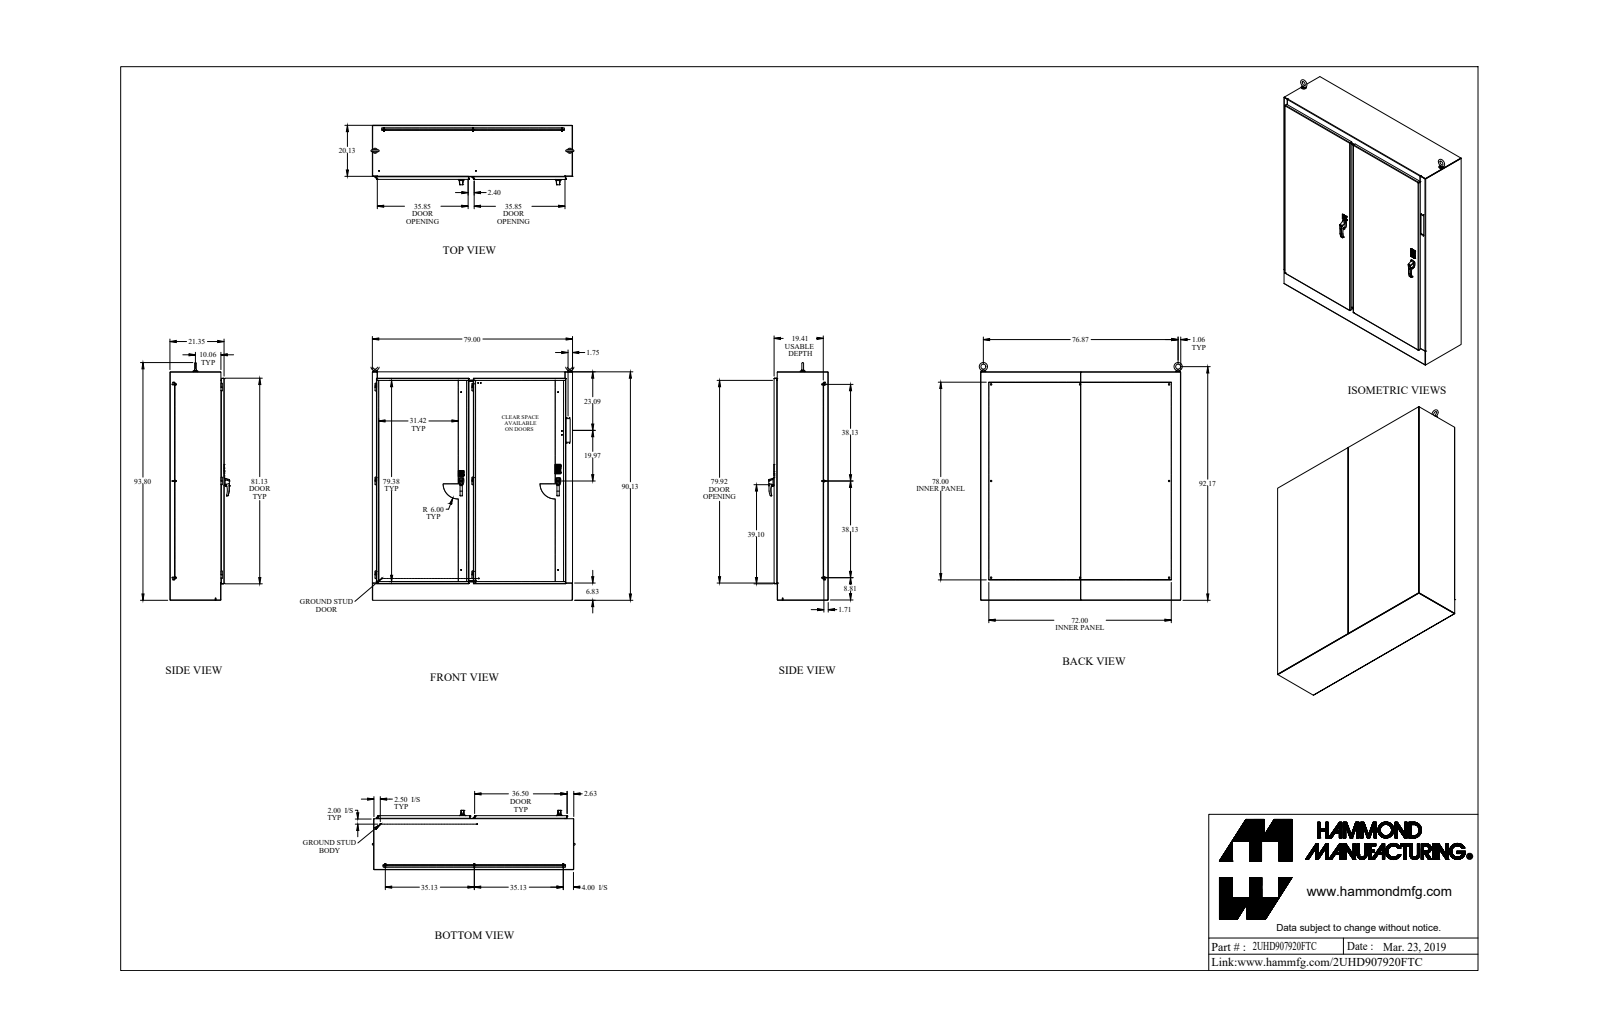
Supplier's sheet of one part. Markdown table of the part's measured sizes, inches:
| quantity | value |
| --- | --- |
| part name | 2UHD907920FTC |
| STEP written by | SolidWorks 2018 (AUTOMOTIVE_DESIGN) |
| units | inches |
| bodies | 215 solids, 3044 faces (1772 planar, 898 cylindrical, 374 other) |
| overall size | 93.799 × 80.122 × 23.466 |
| volume | 5 988 in³ |
| surface area | 62 430 in² |
| round holes (diameter × count) | 0.196 × 12, 0.281 × 11, 0.307 × 11, 0.25 × 10, 0.35 × 8, 0.257 × 6, 0.313 × 6, 0.445 × 5, 0.28 × 4, 0.282 × 4, 0.375 × 4, 0.39 × 4 |
| round bosses / shafts (diameter × count) | 0.25 × 19, 1 × 14, 0.65 × 9, 0.375 × 9, 0.33 × 9, 0.281 × 8, 0.75 × 6, 0.53 × 6 |
| partial cylindrical surfaces (radius × count) | 0.125 × 62, 0.06 × 53, 0.5 × 38, 0.185 × 32, 0.03 × 28, 0.017 × 16, 0.018 × 16, 0.032 × 12 |
| main face-to-face distances | 0.125, 0.072, 19.431, 21.369, 21.243, 1.937, 1.812, 1.865, 1.74, 19.503 |
| hole center spacings | 38.249, 1, 2, 1.126, 1.287, 38.266, 38.25, 70.25 |
